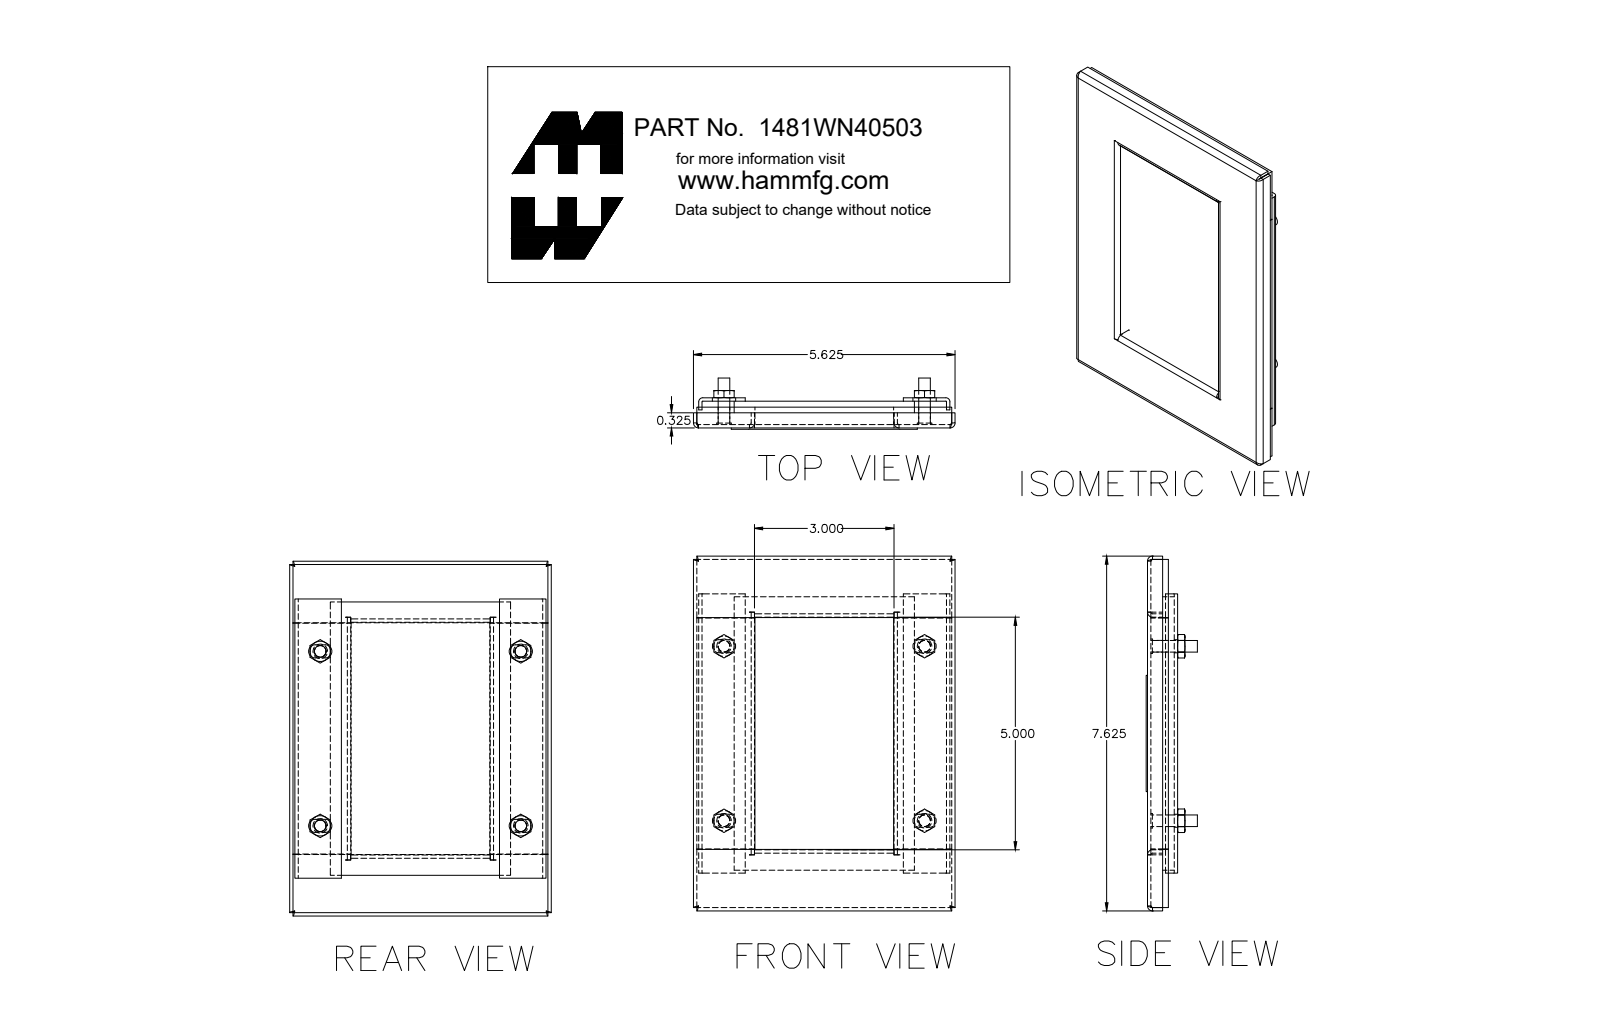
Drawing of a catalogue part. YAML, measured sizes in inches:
part_name: "1481WN40503_Default"
step_written_by: "SolidWorks 2019 (CONFIG_CONTROL_DESIGN)"
units: inches
bodies: {solids: 12, faces: 228, planar: 116, cylindrical: 52, other: 60}
overall_size: [7.625, 5.625, 1.072]
volume: 9.629
surface_area: 164.2
round_holes:
  - {diameter: 0.25, count: 4}
  - {diameter: 0.328, count: 4}
round_bosses_or_shafts:
  - {diameter: 0.313, count: 4}
  - {diameter: 0.25, count: 4}
partial_cylinders:
  - {radius: 0.036, count: 8}
  - {radius: 0.108, count: 8}
  - {radius: 0.016, count: 2}
  - {radius: 0.088, count: 2}
face_to_face_distances: [0.072, 0.25, 0.253, 0.503, 0.325, 0.575, 0.575, 0.647, 0.322, 0.072]
hole_center_spacings: [4.313, 3.75, 5.715, 5.715, 5.715, 3.749, 3.749, 3.751]
